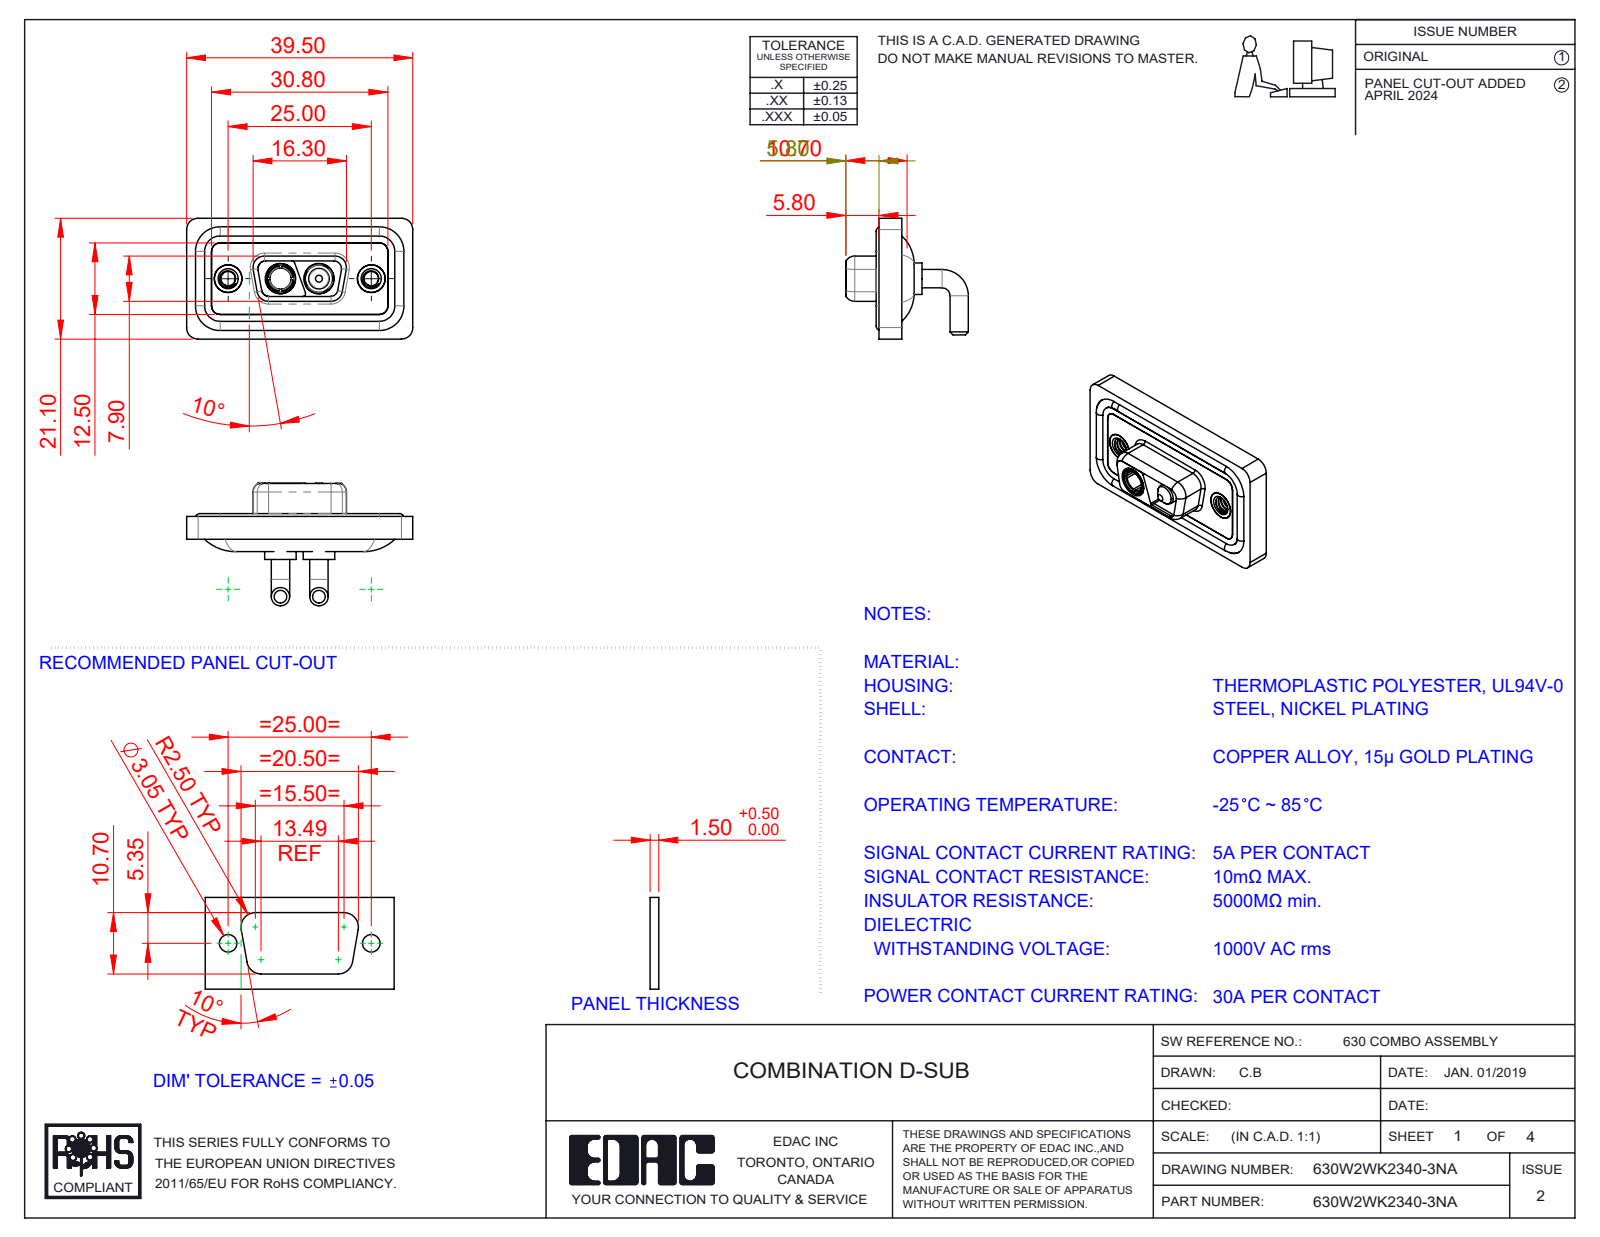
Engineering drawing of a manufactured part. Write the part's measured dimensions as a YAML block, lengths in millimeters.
part_name: "630Combo Shell Rear_09 Contacts; 630Combo Waterproof Housing_09 Contacts; 630Combo Housing_2WK2; 630W2WK2340-3NA (+4 more)"
step_written_by: "SolidWorks 2023 (CONFIG_CONTROL_DESIGN)"
units: millimeters
bodies: {solids: 11, faces: 502, planar: 144, cylindrical: 233, other: 125}
overall_size: [39.5, 21.4, 21.1]
volume: 4755
surface_area: 7534
round_holes:
  - {diameter: 4.85, count: 4}
  - {diameter: 2.5, count: 2}
  - {diameter: 4, count: 2}
  - {diameter: 4.05, count: 2}
  - {diameter: 5, count: 2}
  - {diameter: 5.3, count: 2}
  - {diameter: 3.7, count: 1}
round_bosses_or_shafts:
  - {diameter: 3.2, count: 4}
  - {diameter: 1.6, count: 4}
  - {diameter: 5.5, count: 2}
  - {diameter: 5.2, count: 2}
  - {diameter: 4.95, count: 2}
  - {diameter: 4.8, count: 2}
  - {diameter: 4.75, count: 2}
  - {diameter: 3.75, count: 2}
partial_cylinders:
  - {radius: 1.5, count: 18}
  - {radius: 2, count: 18}
  - {radius: 1.35, count: 8}
  - {radius: 1.6, count: 8}
  - {radius: 0.5, count: 6}
  - {radius: 0.25, count: 4}
  - {radius: 0.6, count: 4}
  - {radius: 0.65, count: 4}
face_to_face_distances: [0.4, 1.1, 2.9, 1.8, 2.5, 1.6, 3.1, 1.5, 2.1, 3.7]
hole_center_spacings: [9.14, 15.86, 6.72, 25]
